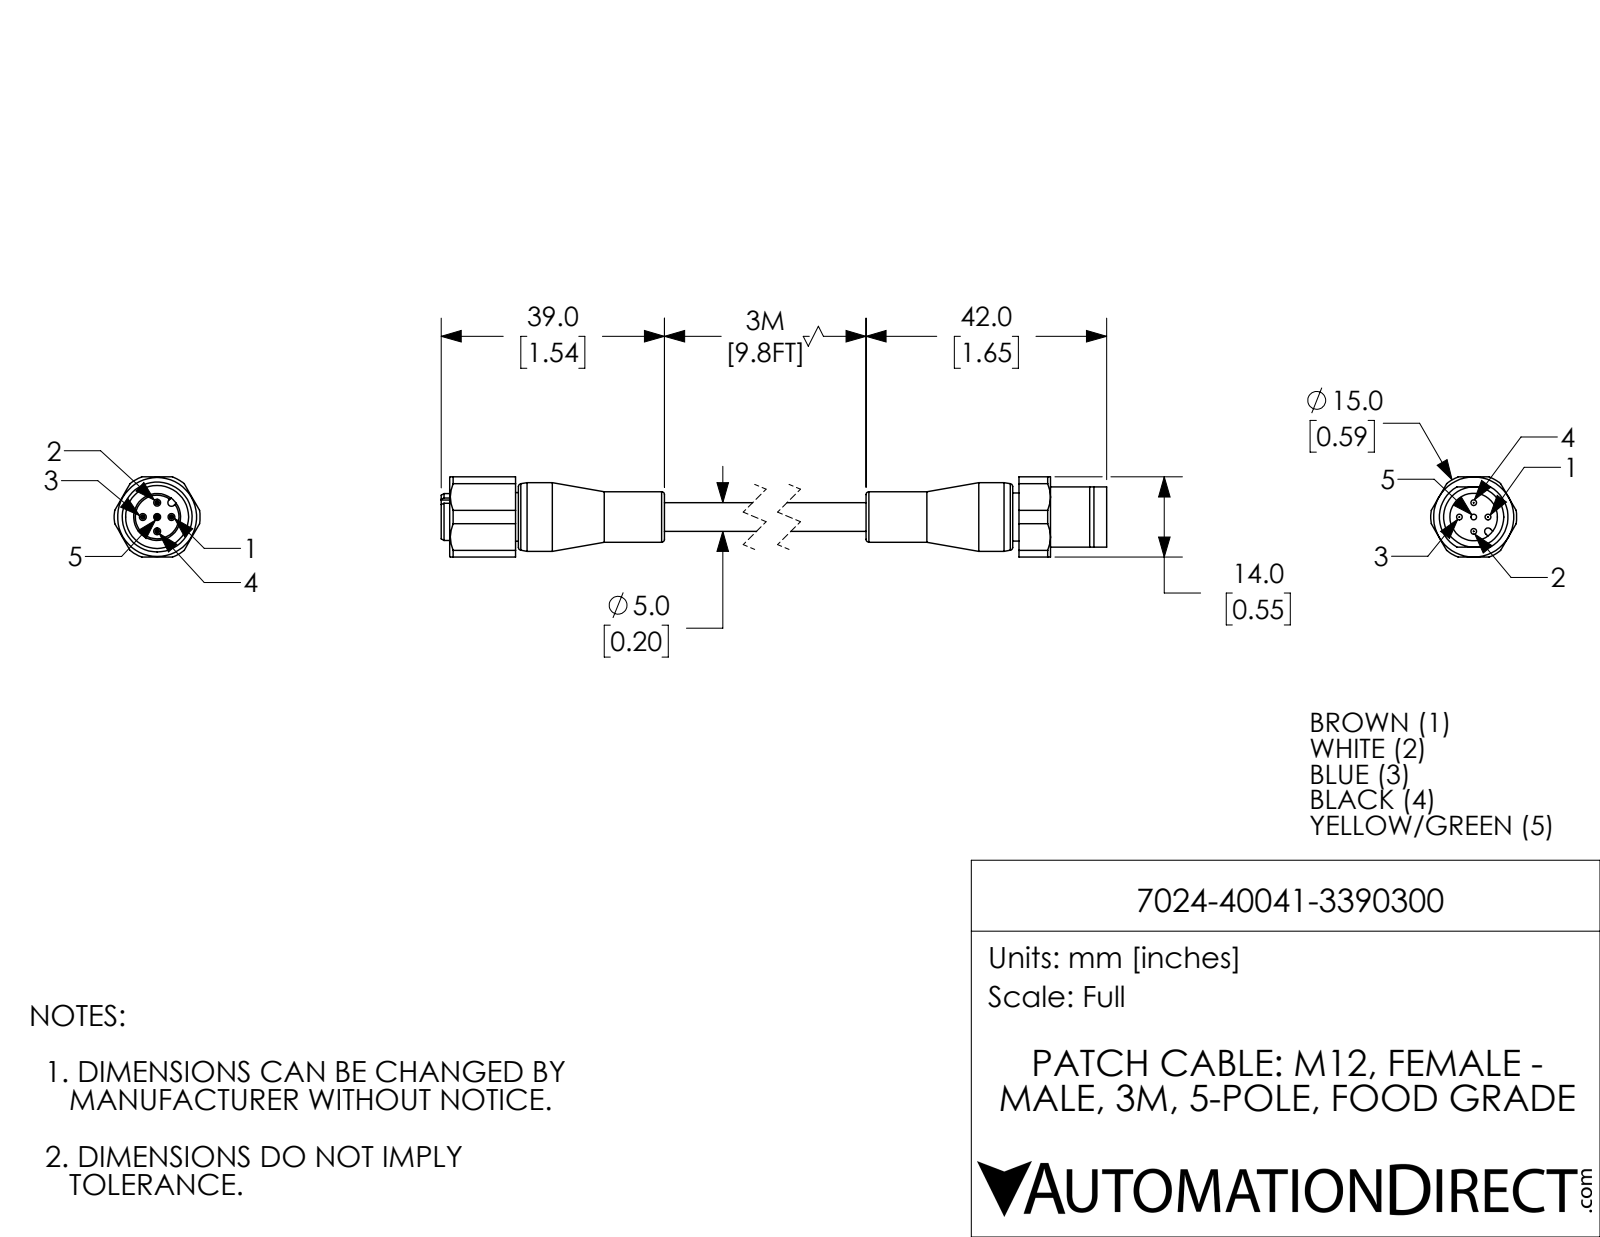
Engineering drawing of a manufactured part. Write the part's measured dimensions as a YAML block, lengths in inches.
part_name: "7024-40041-3390300_MALE; 7024-40041-3390300; 7024-40041-3390300_FEMALE"
step_written_by: "SolidWorks 2018 (AUTOMOTIVE_DESIGN)"
units: inches
bodies: {solids: 2, faces: 148, planar: 43, cylindrical: 62, other: 43}
overall_size: [5.165, 0.591, 0.551]
volume: 0.491
surface_area: 7.892
round_holes:
  - {diameter: 0.047, count: 5}
  - {diameter: 0.327, count: 1}
  - {diameter: 0.433, count: 1}
round_bosses_or_shafts:
  - {diameter: 0.039, count: 5}
  - {diameter: 0.472, count: 1}
  - {diameter: 0.413, count: 1}
  - {diameter: 0.346, count: 1}
  - {diameter: 0.335, count: 1}
  - {diameter: 0.331, count: 1}
  - {diameter: 0.323, count: 1}
  - {diameter: 0.197, count: 1}
partial_cylinders:
  - {radius: 0.024, count: 1}
  - {radius: 0.026, count: 1}
  - {radius: 0.295, count: 1}
face_to_face_distances: [0.551, 4.051, 0.069, 0.482, 4.461, 0.295, 0.217, 4.303, 0.252, 4.268]
hole_center_spacings: [0.098, 0.139, 0.197]
